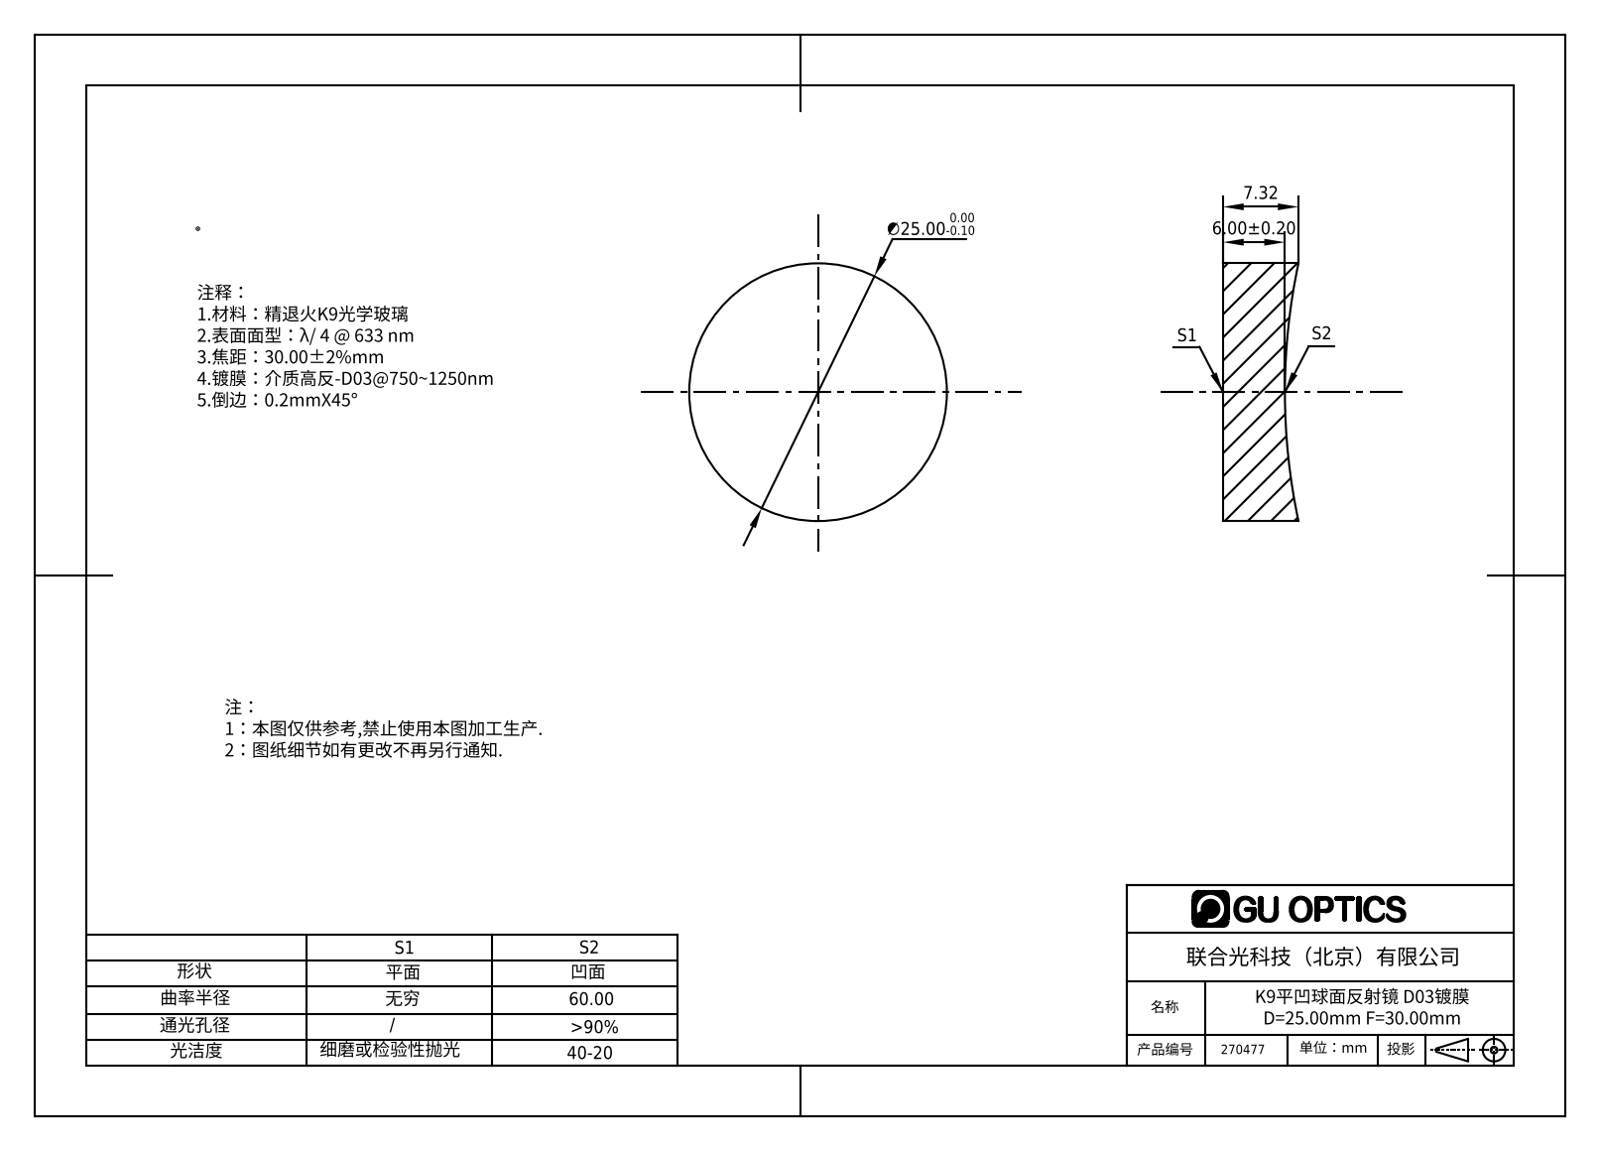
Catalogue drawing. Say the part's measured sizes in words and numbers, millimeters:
The part is named "270022". Its 3-D file was written by "SolidWorks 2016 (AUTOMOTIVE_DESIGN)". It is 1 solid with 5 faces: 1 planar, 2 cylindrical and 2 other. Overall it measures 25 by 25 by 7.32 millimeters. Its volume is 3 267 cubic millimeters and its surface area 1 562 square millimeters. Round bosses or shafts: 1 of diameter 25.
